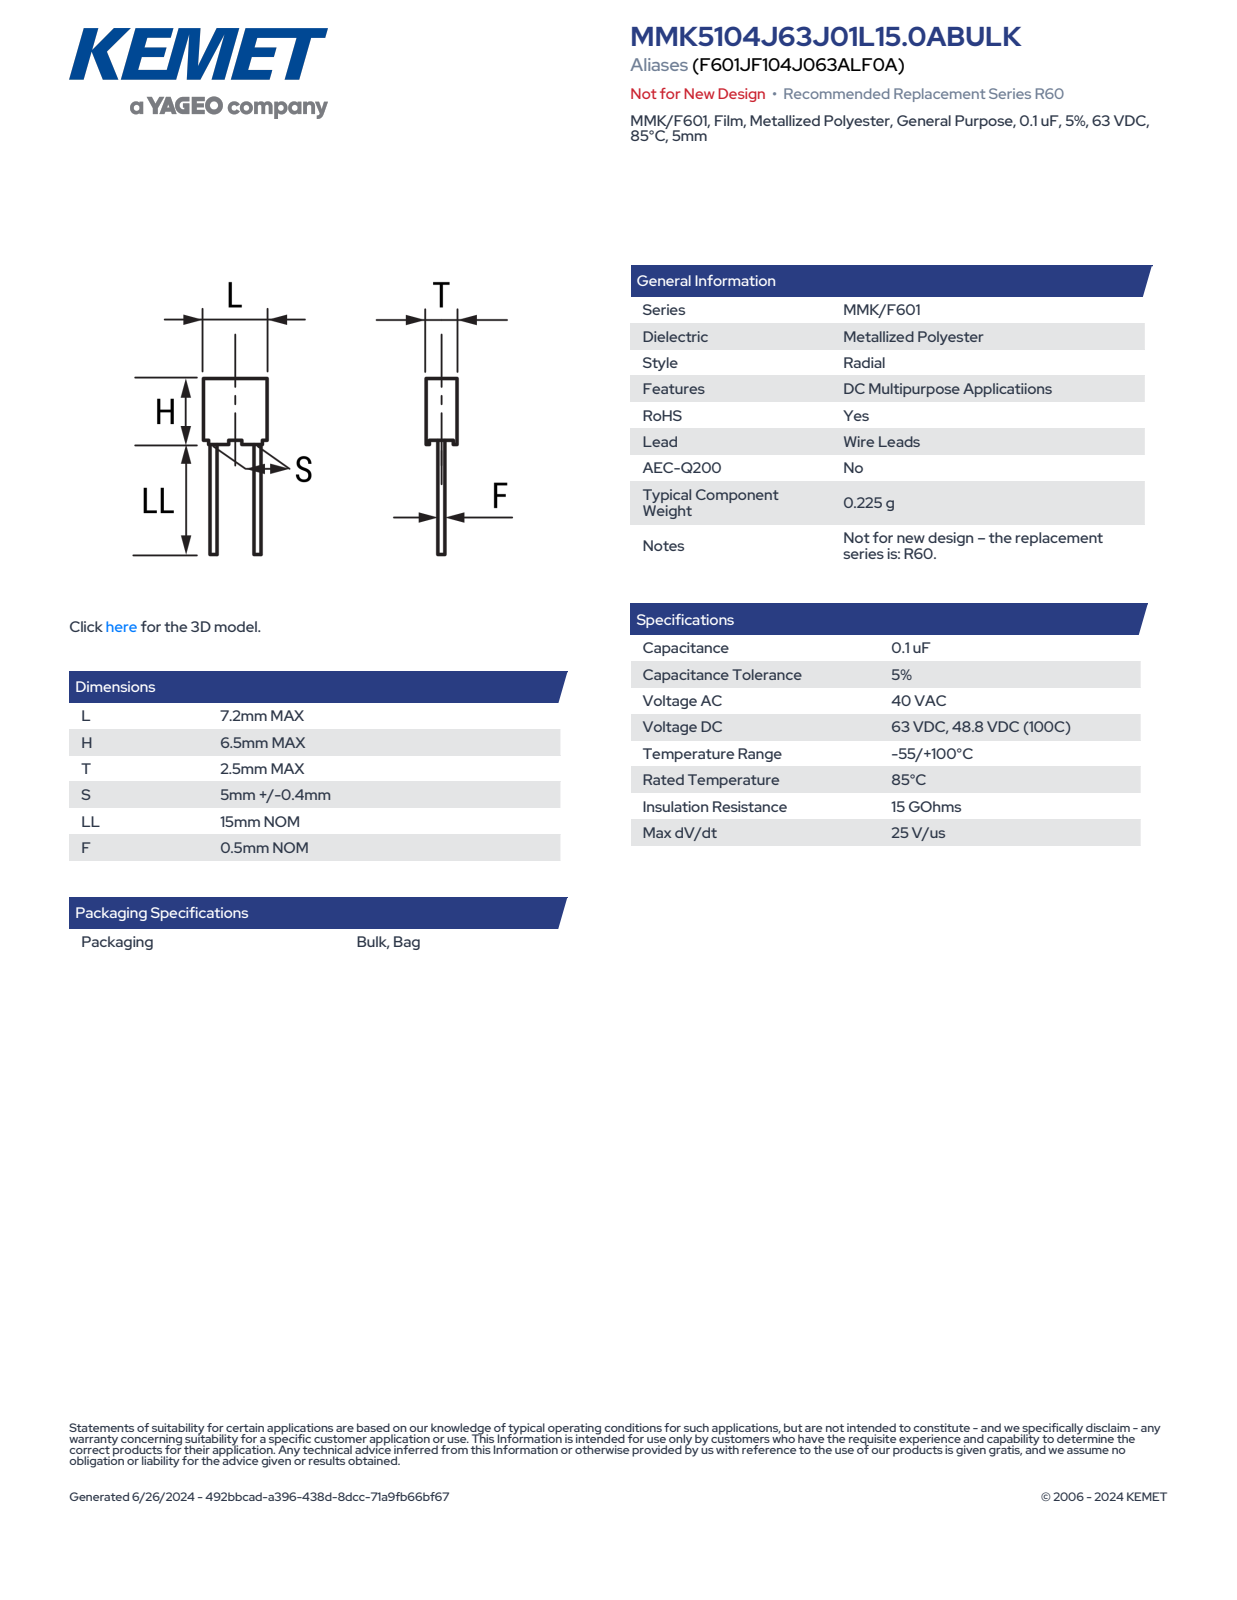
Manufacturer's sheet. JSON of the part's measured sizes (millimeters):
{"part_name": "CFR_RB3_7.2X6.5X2.5_L7.2H6.5T2.5S5LL15F0.5", "step_written_by": "SolidWorks 2014 (AUTOMOTIVE_DESIGN)", "units": "millimeters", "bodies": {"solids": 4, "faces": 85, "planar": 77, "cylindrical": 8, "other": 0}, "overall_size": [21.5, 7.2, 2.5], "volume_mm3": 112, "surface_area_mm2": 223, "round_bosses_or_shafts": [[0.5, 2]], "partial_cylinders_radius": [[0.5, 4]], "face_to_face_distances": [2.5, 7.2, 5.75, 2.26, 2.02, 0.75, 6.5, 6.96, 6.72, 0.53]}
